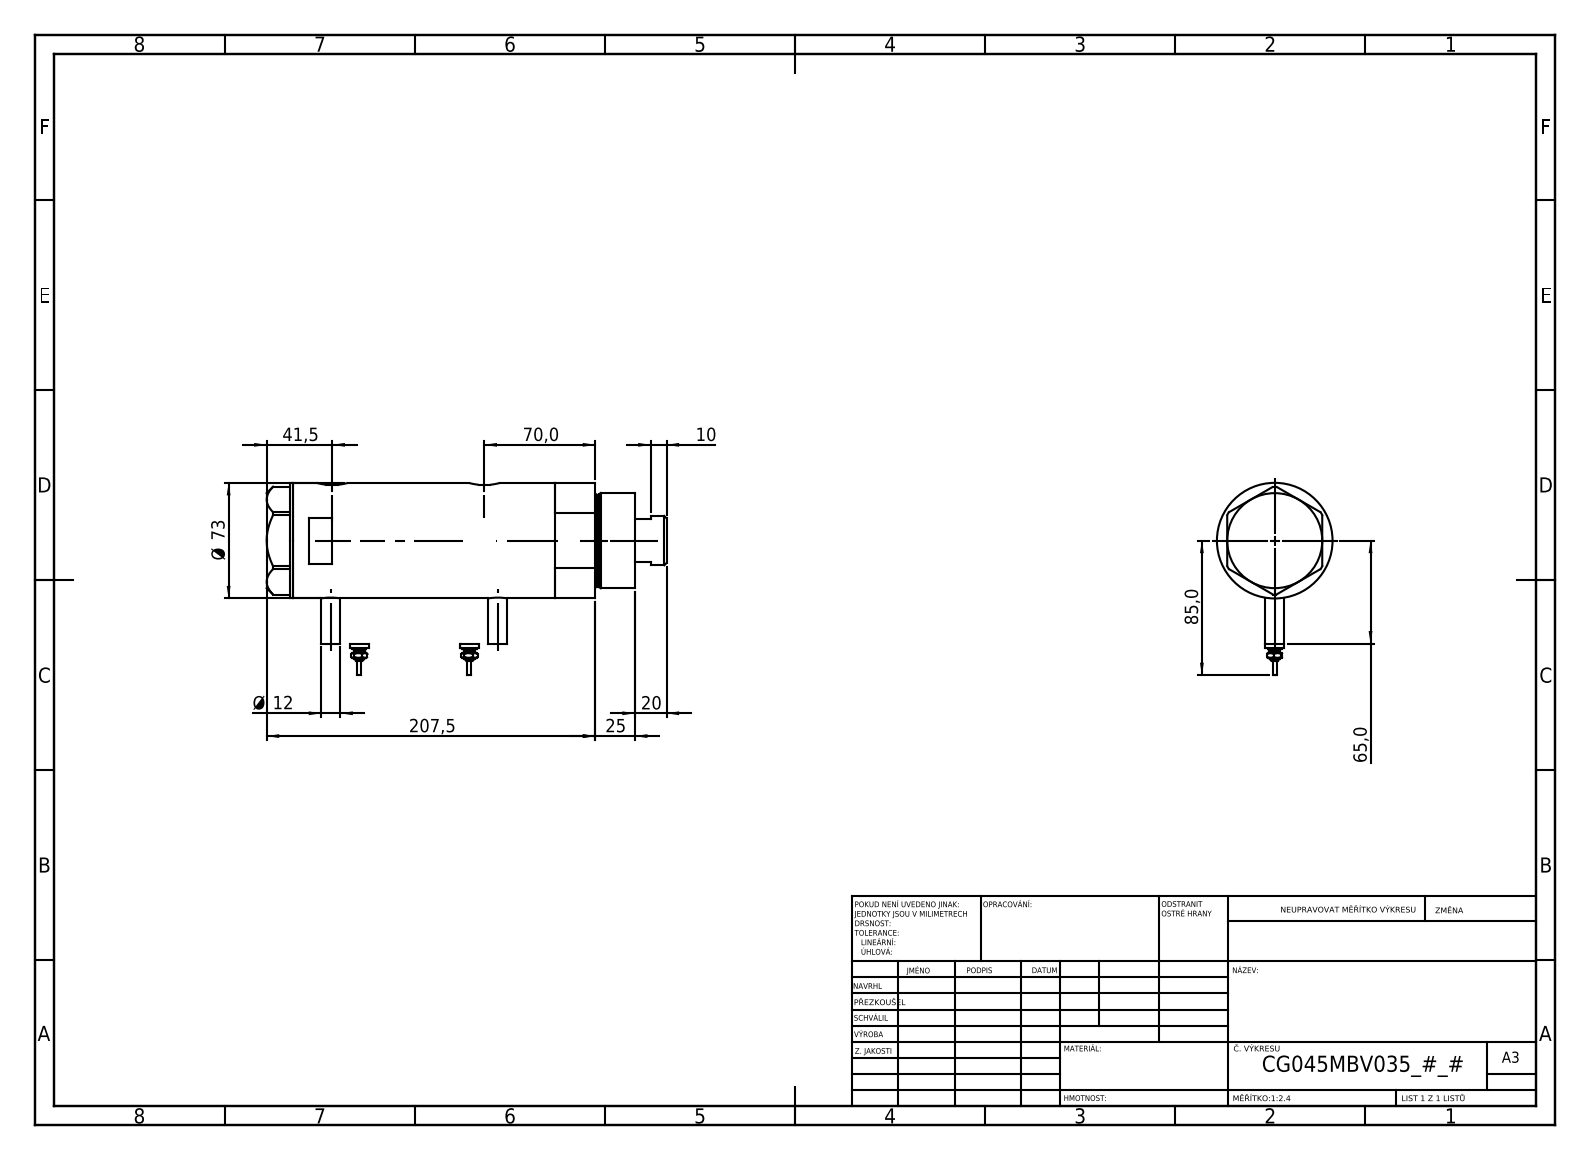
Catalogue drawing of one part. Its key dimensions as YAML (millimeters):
part_name: "V270CG_MIDDLE; V270CG_FRONT; V270CG_BACK; Switch (+1 more)"
step_written_by: "SolidWorks 2019 (CONFIG_CONTROL_DESIGN)"
units: millimeters
bodies: {solids: 6, faces: 212, planar: 77, cylindrical: 71, other: 64}
overall_size: [252.5, 121.5, 73]
volume: 903952
surface_area: 152342
round_holes:
  - {diameter: 12.5, count: 2}
  - {diameter: 13.16, count: 2}
  - {diameter: 10.5, count: 1}
  - {diameter: 32, count: 1}
  - {diameter: 33.5, count: 1}
  - {diameter: 45, count: 1}
  - {diameter: 48, count: 1}
  - {diameter: 64, count: 1}
round_bosses_or_shafts:
  - {diameter: 12, count: 4}
  - {diameter: 9, count: 2}
  - {diameter: 7, count: 2}
  - {diameter: 4.5, count: 2}
  - {diameter: 2.5, count: 2}
  - {diameter: 73, count: 1}
  - {diameter: 60, count: 1}
  - {diameter: 58, count: 1}
partial_cylinders:
  - {radius: 10, count: 2}
face_to_face_distances: [95, 121, 26, 16.5, 42.5, 137.5, 60, 2, 216, 232.5]
hole_center_spacings: [1, 8.5, 96, 97, 104.5, 105.5]
